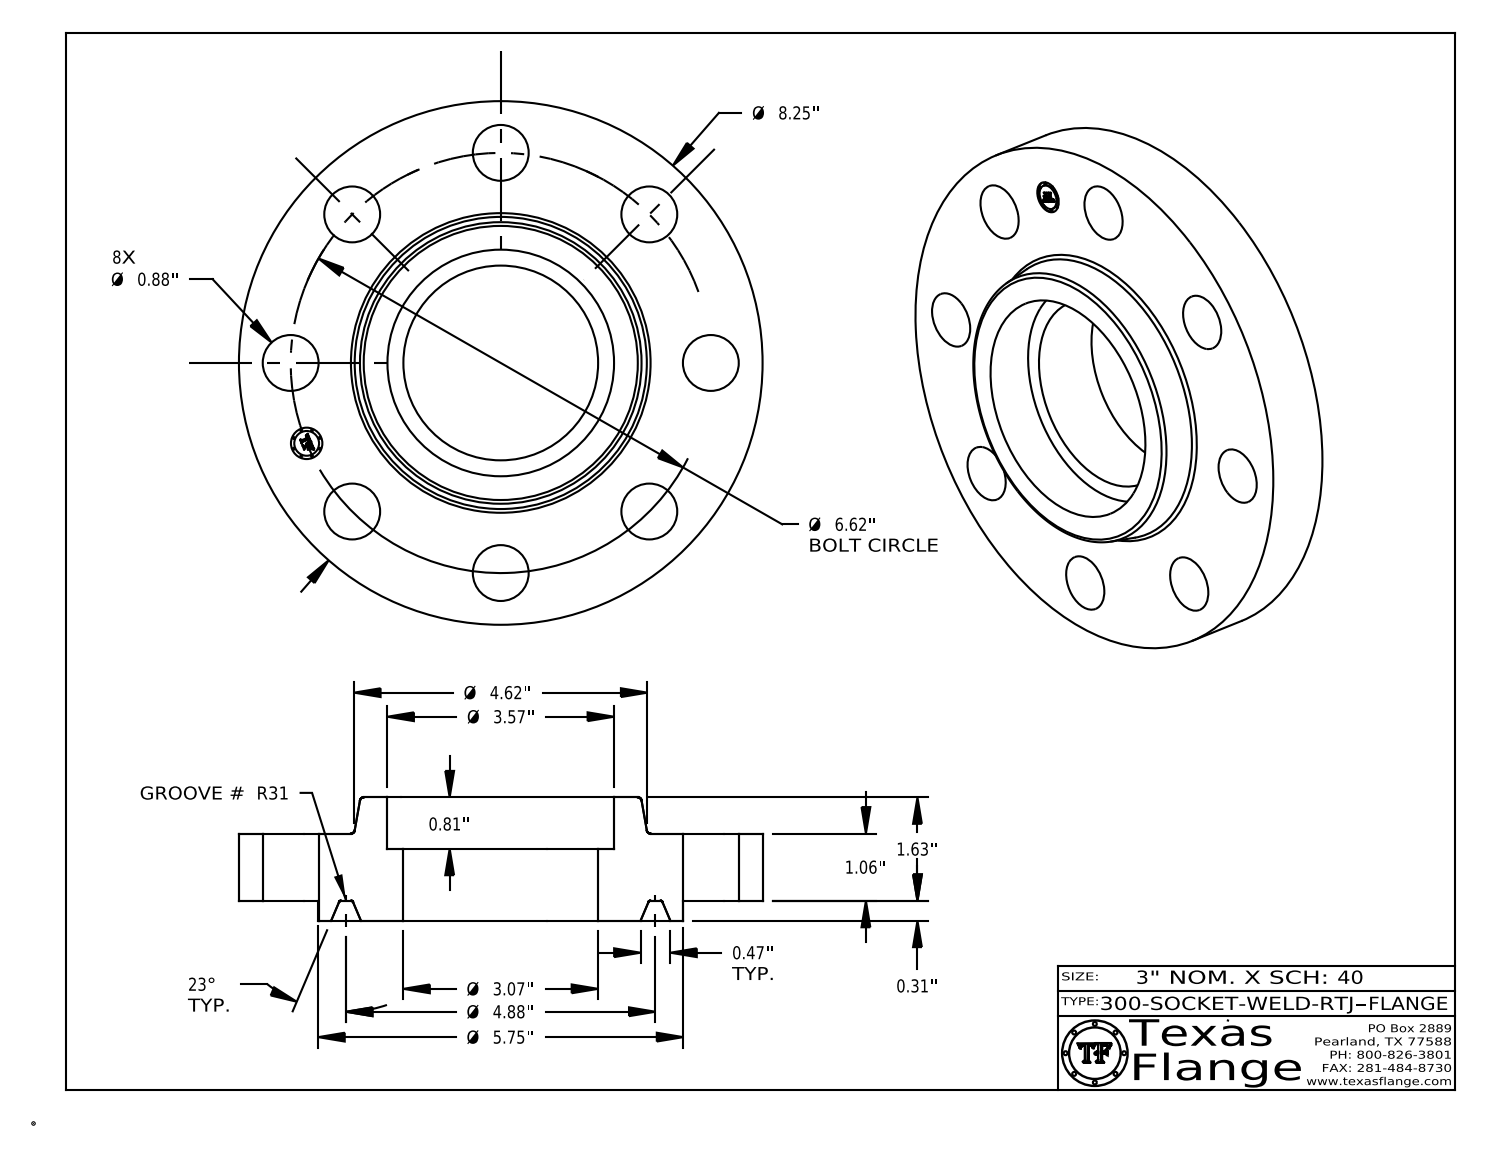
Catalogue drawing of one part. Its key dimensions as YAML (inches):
part_name: "300-SOCKET-WELD-RTJ"
step_written_by: "CATIA V5 STEP AP214 (AUTOMOTIVE_DESIGN)"
units: inches
bodies: {solids: 1, faces: 438, planar: 372, cylindrical: 52, other: 14}
overall_size: [8.25, 8.25, 1.943]
volume: 50.68
surface_area: 171.6
round_holes:
  - {diameter: 0.88, count: 8}
  - {diameter: 0.495, count: 1}
  - {diameter: 3.068, count: 1}
  - {diameter: 3.57, count: 1}
round_bosses_or_shafts:
  - {diameter: 0.03, count: 8}
  - {diameter: 8.25, count: 1}
  - {diameter: 5.75, count: 1}
  - {diameter: 0.39, count: 1}
face_to_face_distances: [1.06, 0.313, 1.373, 1.943, 1.63, 0.57, 1.133, 0.82, 0.24, 0.81]
hole_center_spacings: [3.31, 2.533, 6.116, 4.681, 4.681, 1.291, 3.678, 6.493]
